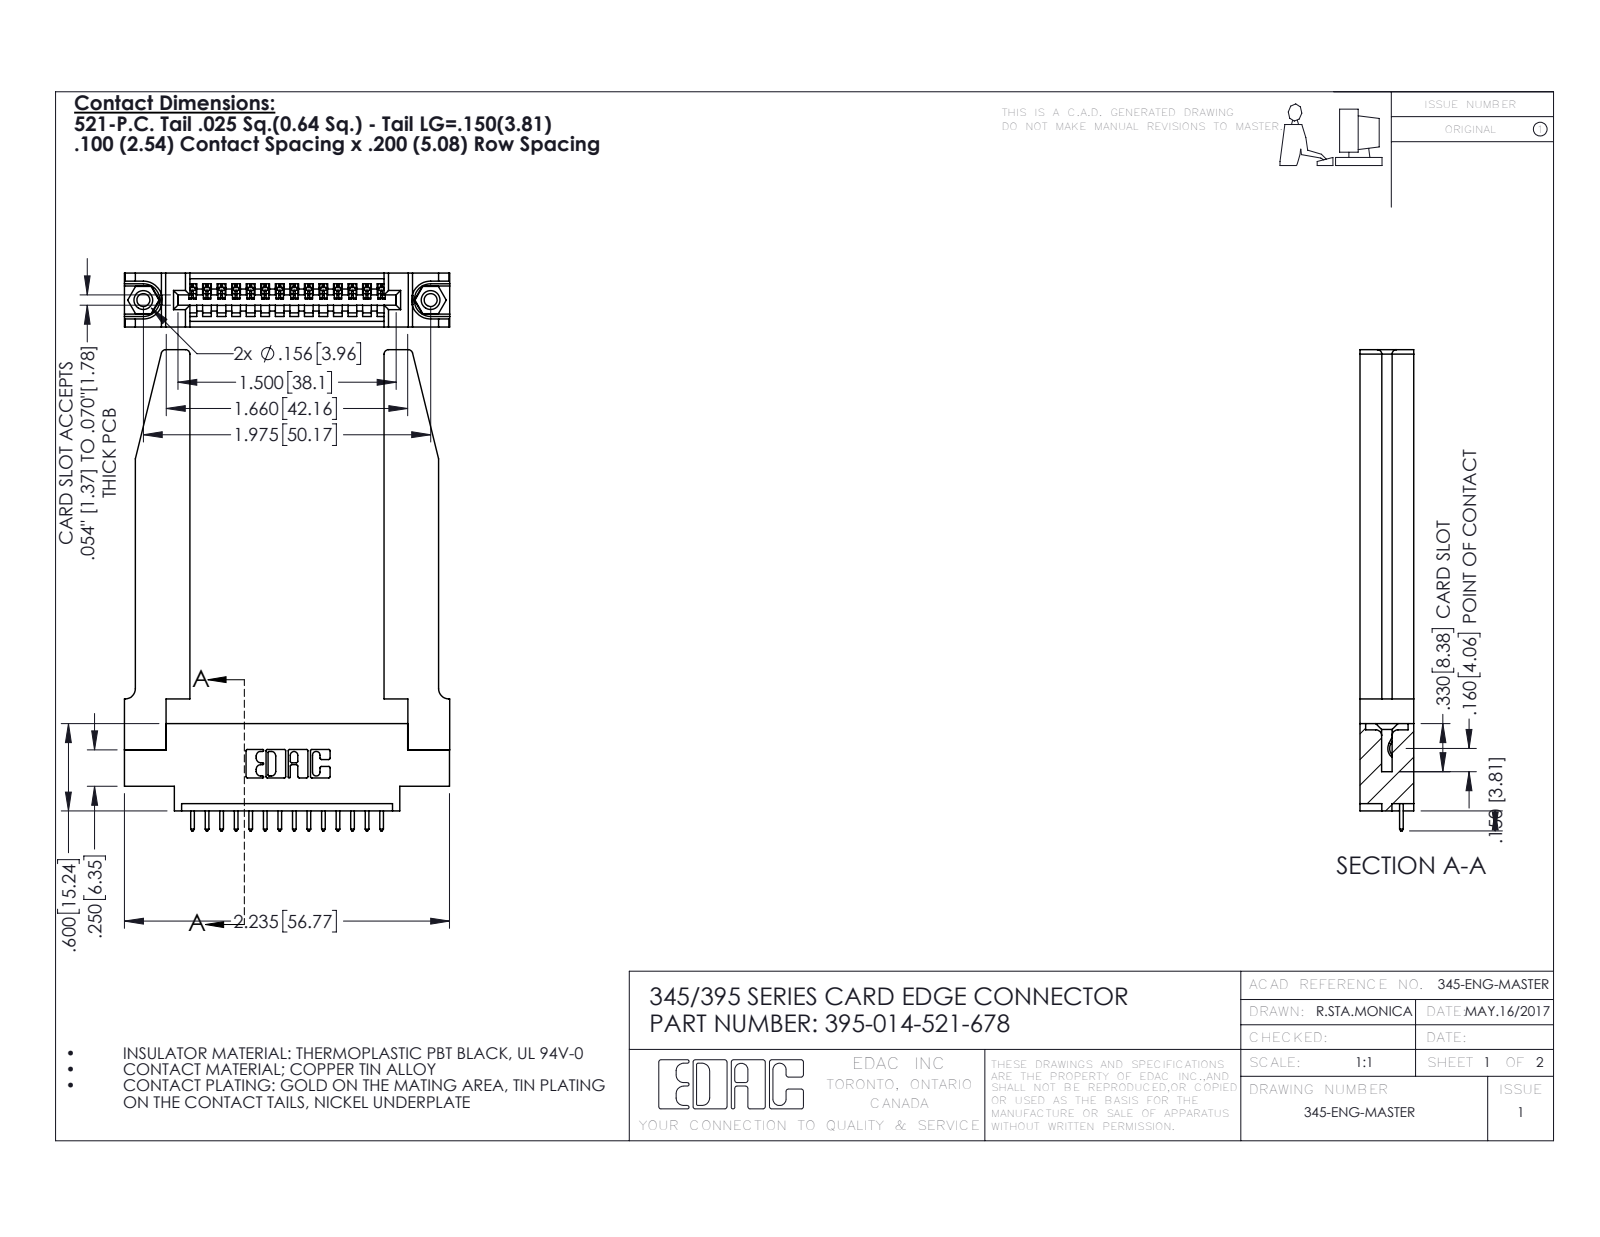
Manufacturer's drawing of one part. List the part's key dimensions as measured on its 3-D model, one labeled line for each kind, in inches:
Part name (STEP PRODUCT): 345-292-001_345-293-121; 345-220-078_345-220-078; 345 Part_0.170 Offset - 0.156 Dia-TH; 345-250-001_345-250-001-102 (+1 more)
STEP written by: SolidWorks 2016 (CONFIG_CONTROL_DESIGN)
Units: inches
Bodies: 19 solids, 1176 faces (786 planar, 338 cylindrical, 52 other)
Overall size (bounding box): 3.307 × 2.236 × 0.37
Volume: 0.78 in³ · Surface area: 20.3 in²
Round holes (diameter × count): ⌀0.089 ×2, ⌀0.125 ×2, ⌀0.156 ×2, ⌀0.064 ×1
Round bosses / shafts (diameter × count): ⌀0.155 ×2
Partial cylindrical surfaces — rounded edges, fillets, slot ends (radius × count): R0.006 ×28, R0.01 ×28, R0.01 ×22, R0.03 ×8, R0.007 ×6, R0.031 ×6, R0.026 ×3, R0.031 ×2
Main face-to-face distances: 0.37, 0.072, 0.298, 0.148, 0.15, 0.22, 0.077, 0.2, 1.335, 0.098
Hole centre spacings: 0.27, 1.742, 1.975
